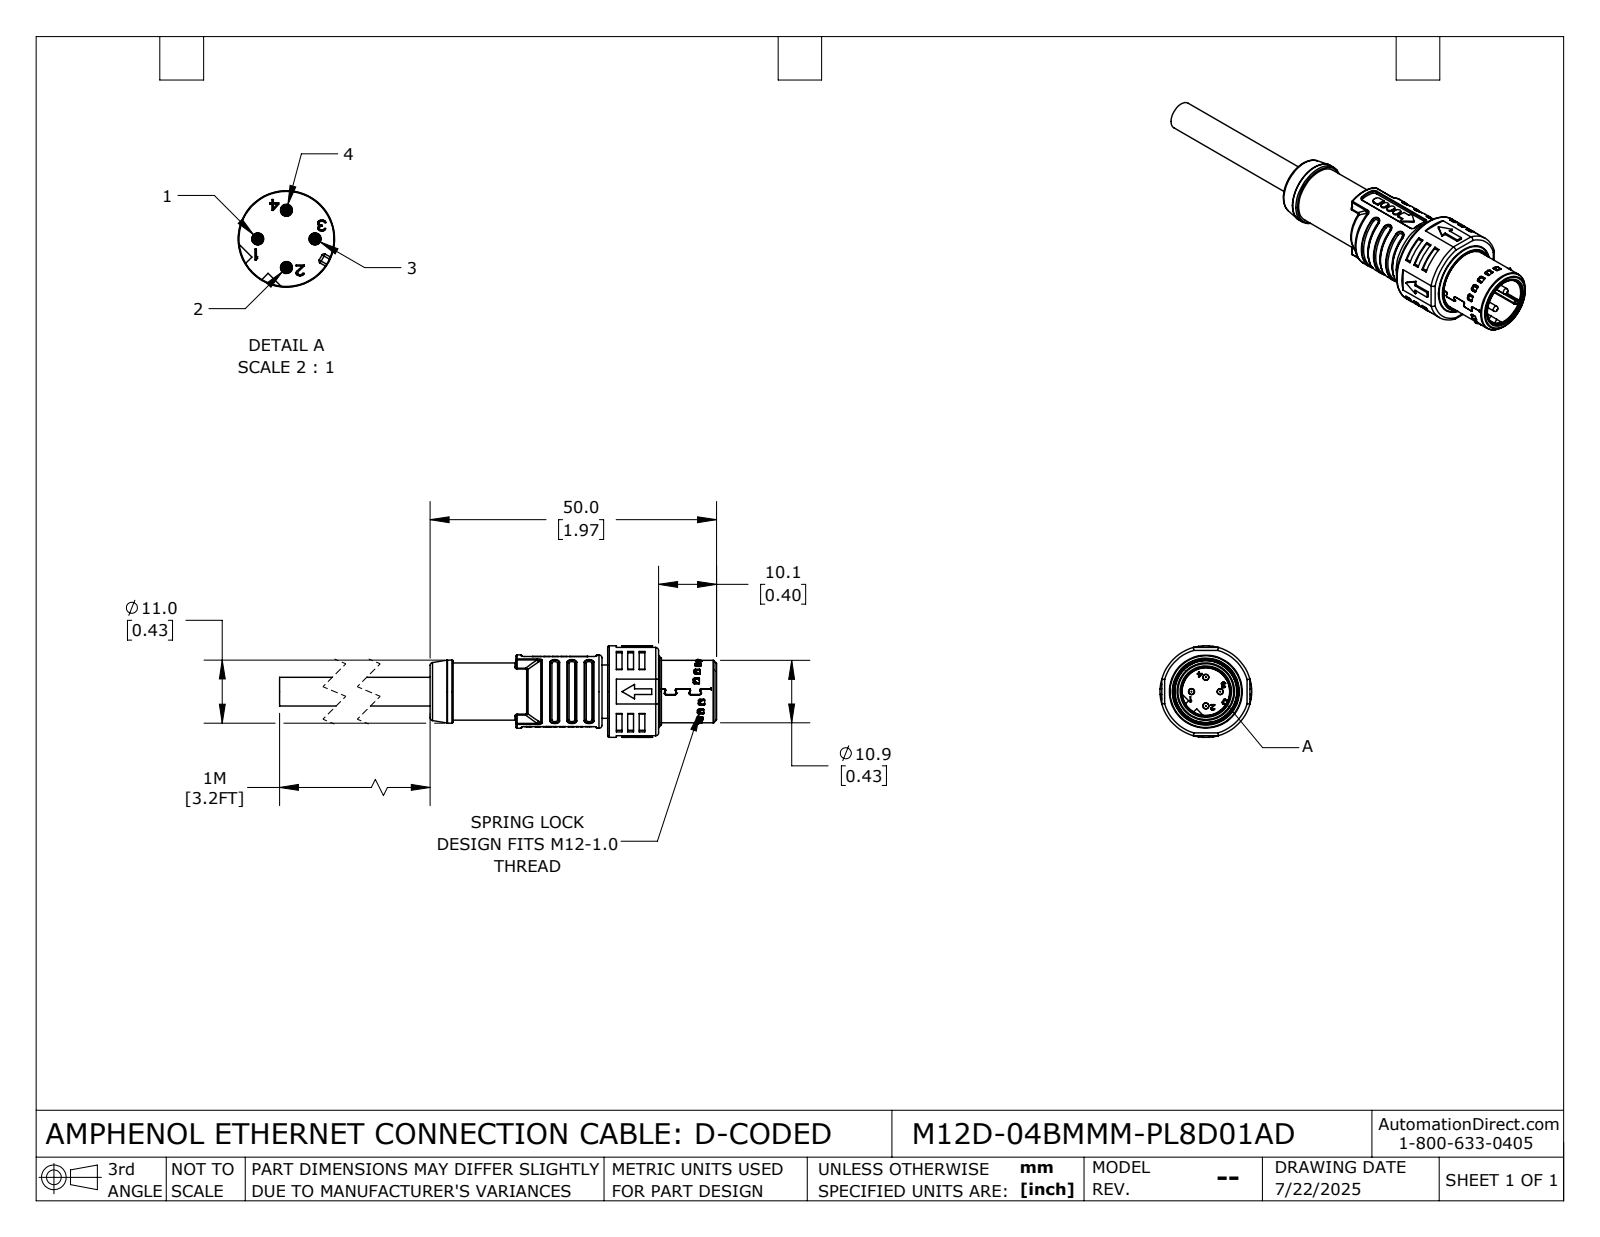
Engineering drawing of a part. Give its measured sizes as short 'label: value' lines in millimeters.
name: M12D-04BMMM-PL8D01AD
written by: SolidWorks 2024 (CONFIG_CONTROL_DESIGN)
unit: mm
bodies: 1 solid, 2139 faces (996 planar, 644 cylindrical, 499 other)
size: 80 × 16 × 16
volume: 5 399 mm³; area: 5 961 mm²
holes: 4× ⌀1.05, 1× ⌀8.3, 1× ⌀9, 1× ⌀10.15, 1× ⌀10.5, 1× ⌀10.9, 1× ⌀11.5, 1× ⌀11.8, 1× ⌀14.2
bosses: 4× ⌀1, 1× ⌀16, 1× ⌀14.1, 1× ⌀12.8, 1× ⌀12.4, 1× ⌀11, 1× ⌀10.45, 1× ⌀10.4
rounds: 119× R0.2, 66× R0.25, 64× R0.3, 44× R0.15, 38× R0.5, 12× R0.13, 11× R0.7, 7× R0.1
face distances: 1, 30, 10.1, 8.9, 2.5, 1.2, 8.6, 32.5, 15.4, 1.5
hole spacings: 2.5, 3.54, 5
